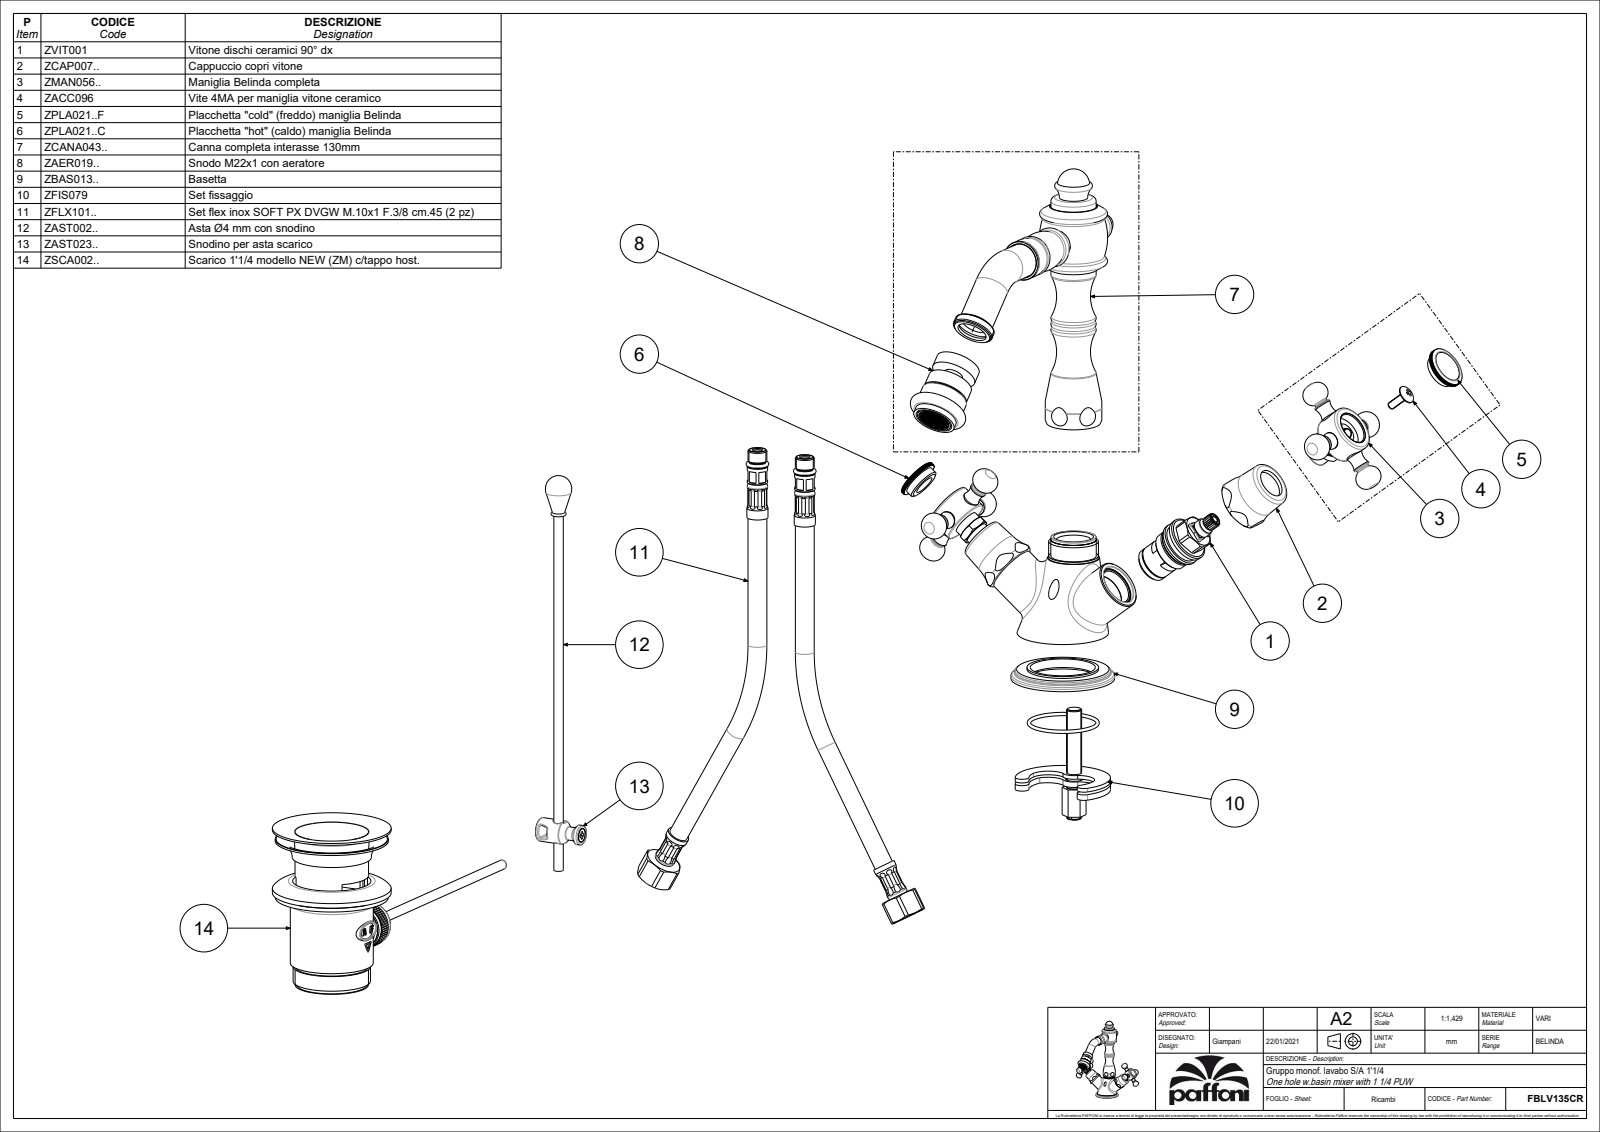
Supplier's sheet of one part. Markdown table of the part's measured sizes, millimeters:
| quantity | value |
| --- | --- |
| part name | FBLV135CR |
| STEP written by | CREO PARAMETRIC BY PTC INC, 2020044 (CONFIG_CONTROL_DESIGN) |
| units | millimeters |
| bodies | 4 solids, 1353 faces (581 planar, 406 cylindrical, 366 other) |
| overall size | 229.4 × 175.57 × 174.66 |
| volume | 227 533 mm³ |
| surface area | 70 923 mm² |
| round holes (diameter × count) | 9 × 4, 11 × 2, 15.5 × 2, 18 × 2, 19 × 2, 21 × 2, 21.5 × 2, 22.8 × 2, 25.5 × 2, 5.5 × 1, 6 × 1, 6.8 × 1 |
| round bosses / shafts (diameter × count) | 9 × 6, 7 × 6, 25 × 3, 26.3 × 2, 24 × 2, 18 × 2, 14 × 2, 13 × 2 |
| partial cylindrical surfaces (radius × count) | 3.5 × 2, 11 × 2 |
| main face-to-face distances | 5, 4.98, 2, 1.3, 57.21, 11.4, 45.81, 1, 29.2, 24.2 |
| hole center spacings | 7, 11.8, 13.38, 13.89, 0.6, 9.5, 11.4, 12 |
